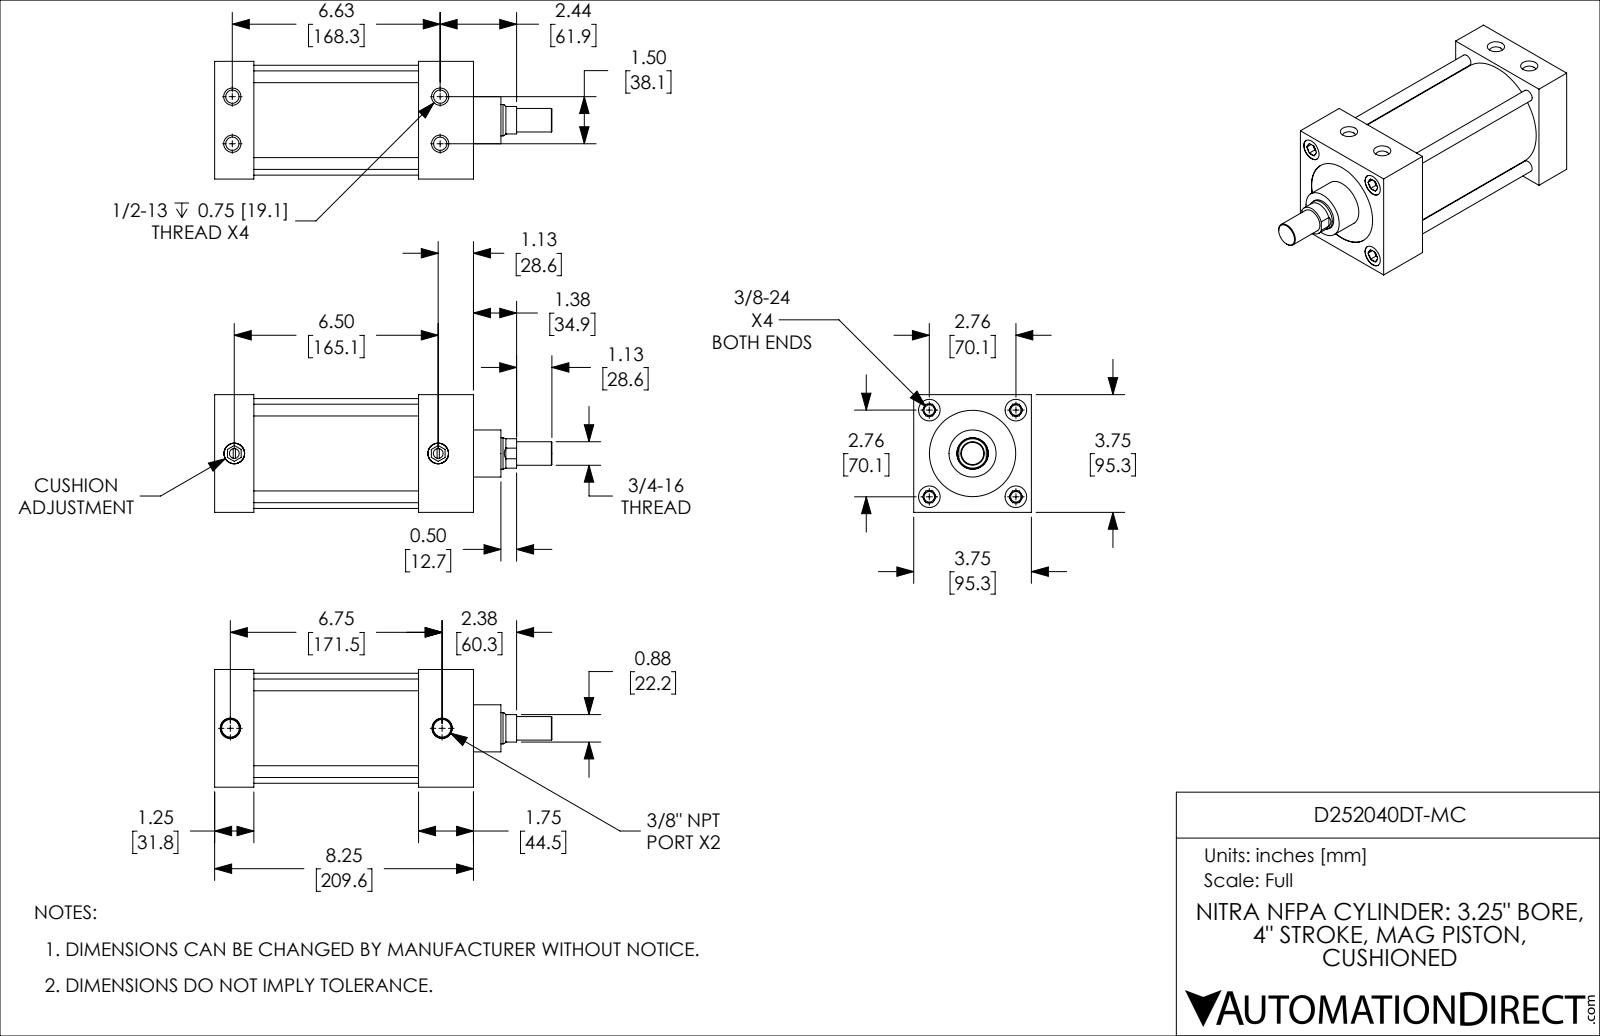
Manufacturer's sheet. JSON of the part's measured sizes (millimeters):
{"part_name": "D252040DT-MC_PISTON_KK1; D252040DT-MC_BODY; D252040DT-MC; D252040DT-MC_CUSHION", "step_written_by": "SolidWorks 2019 (CONFIG_CONTROL_DESIGN)", "units": "millimeters", "bodies": {"solids": 4, "faces": 246, "planar": 90, "cylindrical": 78, "other": 78}, "overall_size": [273.1, 95.3, 95.3], "volume_mm3": 1065000, "surface_area_mm2": 207700, "round_holes": [[8.4, 4], [10.7, 4], [17.4, 4], [7.9, 2], [14.3, 2], [16.7, 2], [25.4, 1], [69.9, 1], [82.6, 1]], "round_bosses_or_shafts": [[9.5, 4], [16.7, 2], [88.9, 1], [82.5, 1], [38.1, 1], [25.4, 1], [19.1, 1]], "partial_cylinders_radius": [[11.9, 1]], "face_to_face_distances": [31.8, 95.3, 165.1, 133.4, 63.5, 101.6, 209.6, 177.8, 146.1, 44.5], "hole_center_spacings": [19.1, 49.6, 70.1, 170.9, 38.1, 99.1, 168.3, 172.5]}
